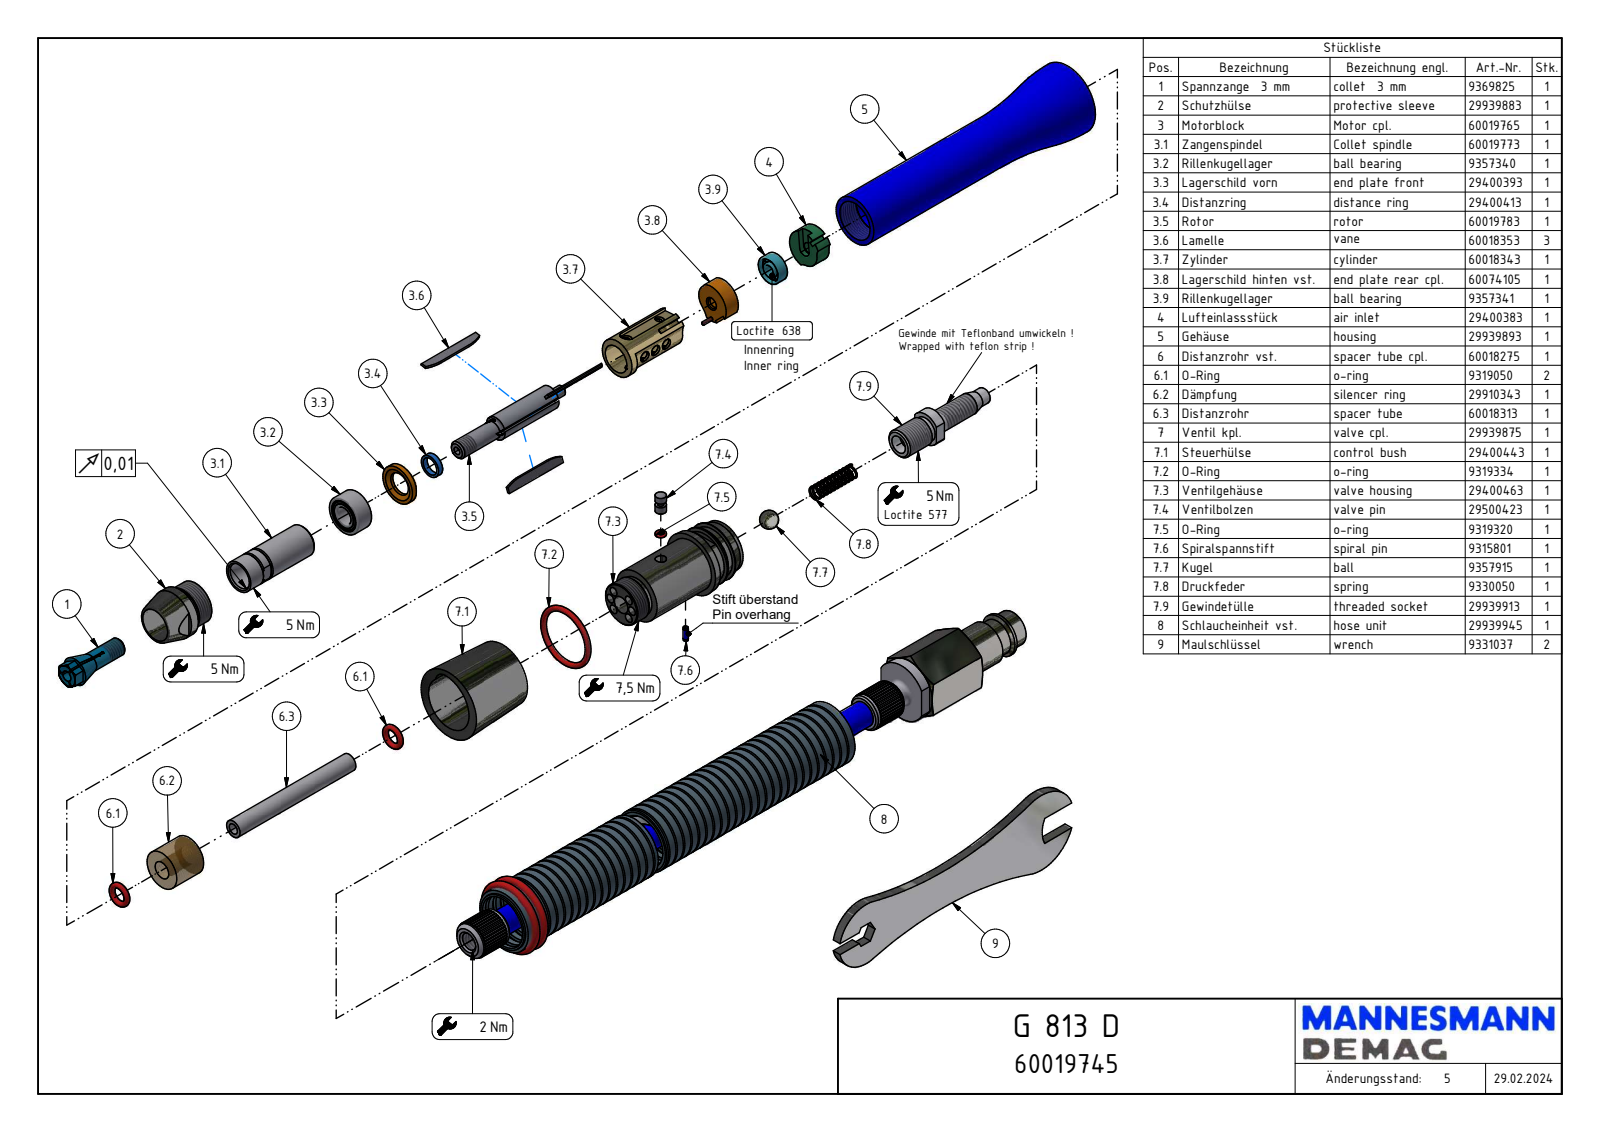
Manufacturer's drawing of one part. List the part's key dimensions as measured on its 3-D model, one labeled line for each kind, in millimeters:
Part name (STEP PRODUCT): G 813 D_60019745
STEP written by: Autodesk Inventor 2008 (AUTOMOTIVE_DESIGN)
Units: millimetres
Bodies: 1 solid, 138 faces (64 planar, 25 cylindrical, 49 other)
Overall size (bounding box): 155.81 × 20.55 × 20.55
Volume: 23 656 mm³ · Surface area: 9 047 mm²
Round holes (diameter × count): ⌀3 ×1, ⌀3.1 ×1, ⌀9.2 ×1
Round bosses / shafts (diameter × count): ⌀16.5 ×1, ⌀14.5 ×1, ⌀14 ×1, ⌀13.5 ×1, ⌀11 ×1, ⌀9 ×1, ⌀7.09 ×1, ⌀6 ×1
Partial cylindrical surfaces — rounded edges, fillets, slot ends (radius × count): R5 ×3, R4.75 ×1
Main face-to-face distances: 10, 102, 0.5, 112, 0.35, 10.35, 101.65, 3, 111, 1
